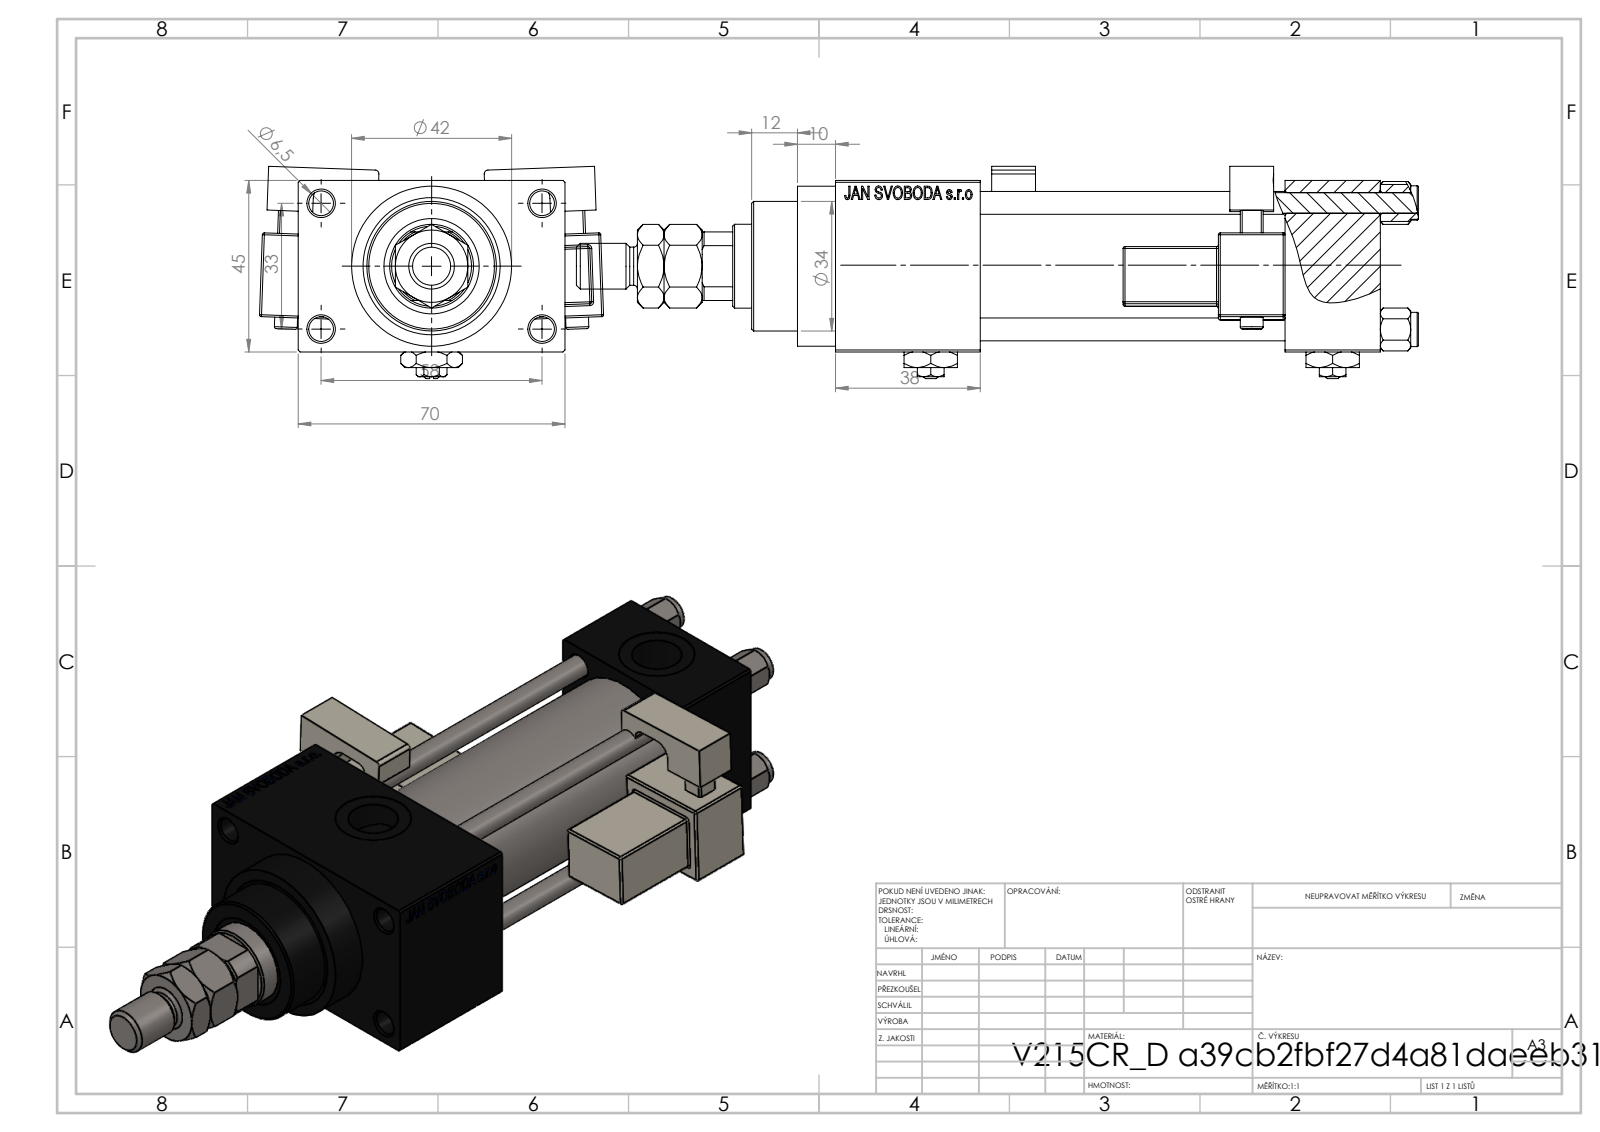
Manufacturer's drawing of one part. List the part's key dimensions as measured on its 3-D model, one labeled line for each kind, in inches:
Part name (STEP PRODUCT): V215CR_VCP_D; V215CR_D_Body; Zatka_pro_OIL_PORT; NUT_M5_D (+4 more)
STEP written by: SolidWorks 2019 (CONFIG_CONTROL_DESIGN)
Units: inches
Bodies: 16 solids, 1411 faces (619 planar, 164 cylindrical, 628 other)
Overall size (bounding box): 8.701 × 3.556 × 2.194
Volume: 19.26 in³ · Surface area: 164.9 in²
Round holes (diameter × count): ⌀0.236 ×4, ⌀0.256 ×4, ⌀0.276 ×2, ⌀0.518 ×2, ⌀0.787 ×2, ⌀0.413 ×1, ⌀0.866 ×1, ⌀0.945 ×1, ⌀0.984 ×1, ⌀1.26 ×1, ⌀1.299 ×1
Round bosses / shafts (diameter × count): ⌀0.354 ×4, ⌀0.236 ×2, ⌀1.654 ×1, ⌀1.496 ×1, ⌀1.339 ×1, ⌀0.472 ×1, ⌀0.394 ×1
Partial cylindrical surfaces — rounded edges, fillets, slot ends (radius × count): R0.02 ×48, R0.039 ×2, R0.098 ×2, R0.157 ×2, R0.413 ×1
Main face-to-face distances: 1.772, 0.984, 0.492, 3.15, 0.118, 2.264, 4.134, 1.496, 4.646, 2.756
Hole centre spacings: 0.488, 0.924, 1.307, 1.314, 1.392, 1.795, 2.219, 1.299
